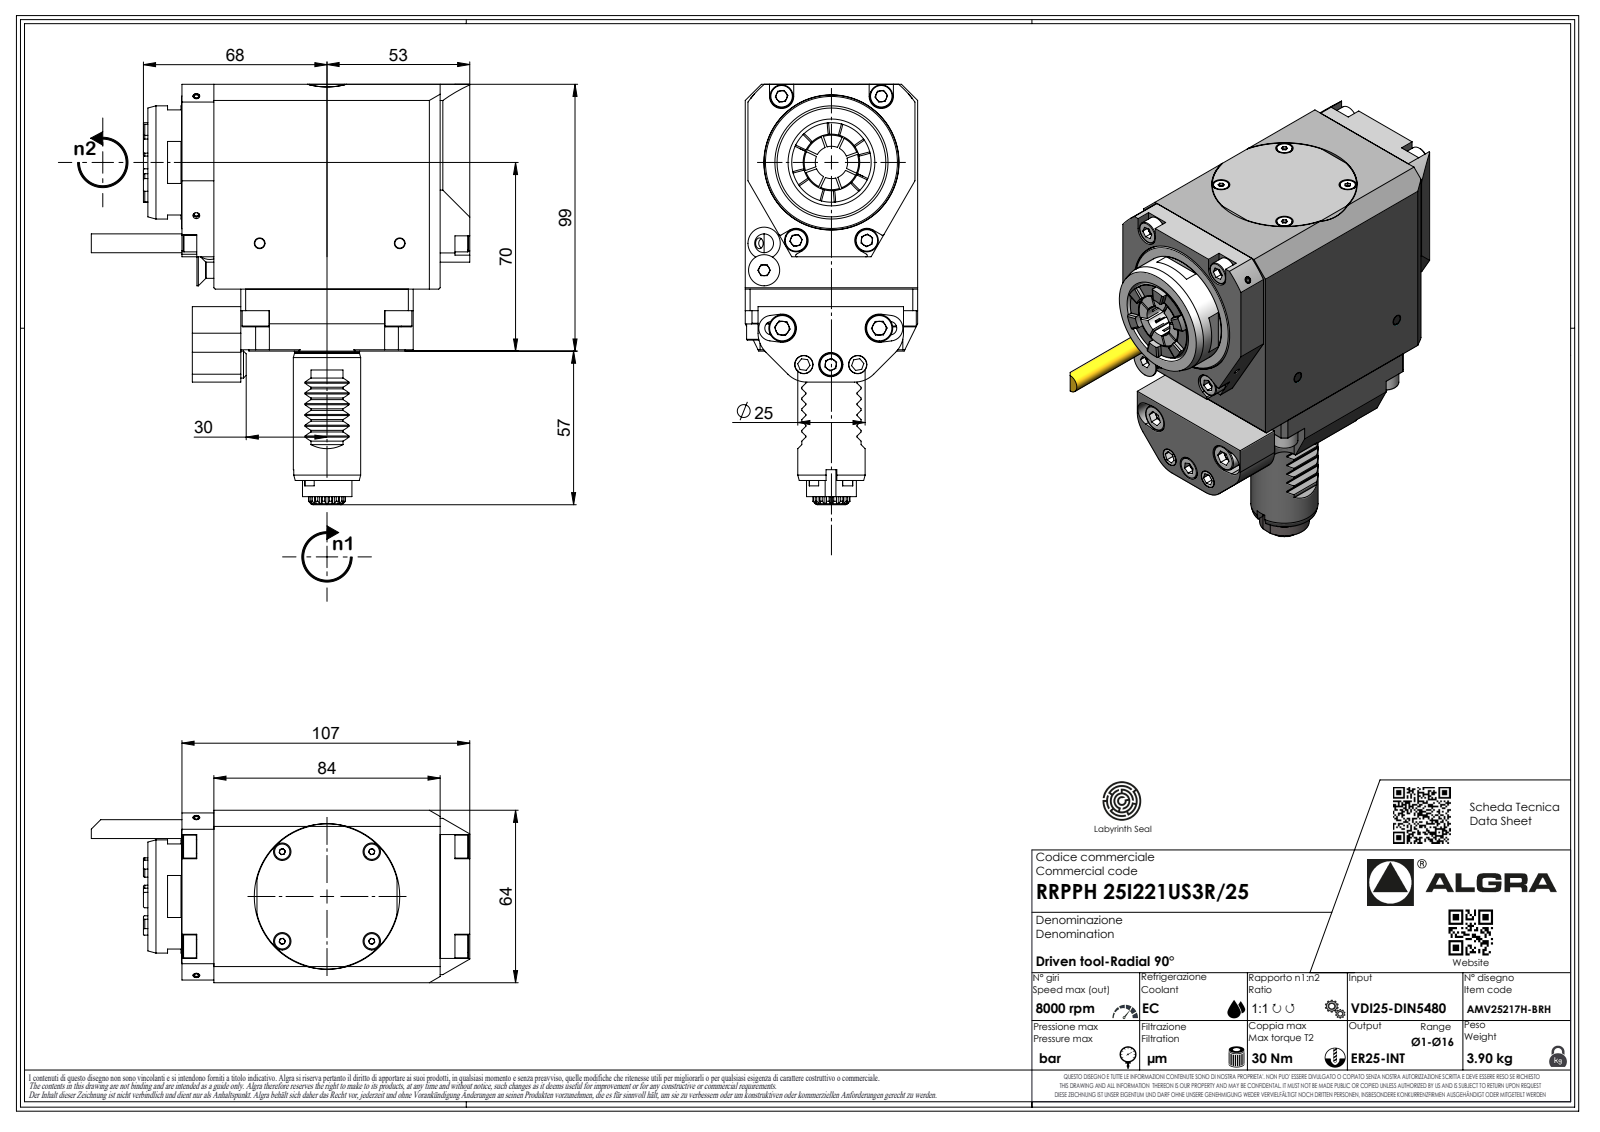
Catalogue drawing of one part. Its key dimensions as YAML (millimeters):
part_name: "RRPPH25I221US3R25"
step_written_by: "SolidWorks 2023 (AUTOMOTIVE_DESIGN)"
units: millimeters
bodies: {solids: 3, faces: 854, planar: 518, cylindrical: 164, other: 172}
overall_size: [156, 142.64, 64]
volume: 630638
surface_area: 59801
round_holes:
  - {diameter: 4, count: 2}
  - {diameter: 12, count: 2}
  - {diameter: 2.1, count: 1}
  - {diameter: 8.8, count: 1}
  - {diameter: 18.7, count: 1}
  - {diameter: 22, count: 1}
round_bosses_or_shafts:
  - {diameter: 42, count: 1}
  - {diameter: 25, count: 1}
  - {diameter: 24.1, count: 1}
  - {diameter: 18.5, count: 1}
  - {diameter: 11, count: 1}
  - {diameter: 7, count: 1}
  - {diameter: 6.37, count: 1}
  - {diameter: 1.7, count: 1}
partial_cylinders:
  - {radius: 0.3, count: 12}
  - {radius: 35, count: 8}
  - {radius: 0.33, count: 7}
  - {radius: 0.52, count: 7}
  - {radius: 3.7, count: 7}
  - {radius: 0.5, count: 6}
  - {radius: 4.5, count: 4}
  - {radius: 5.1, count: 4}
face_to_face_distances: [64, 16.5, 10, 85, 74, 99, 98.5, 34.5, 8, 24.5]
hole_center_spacings: [2]
